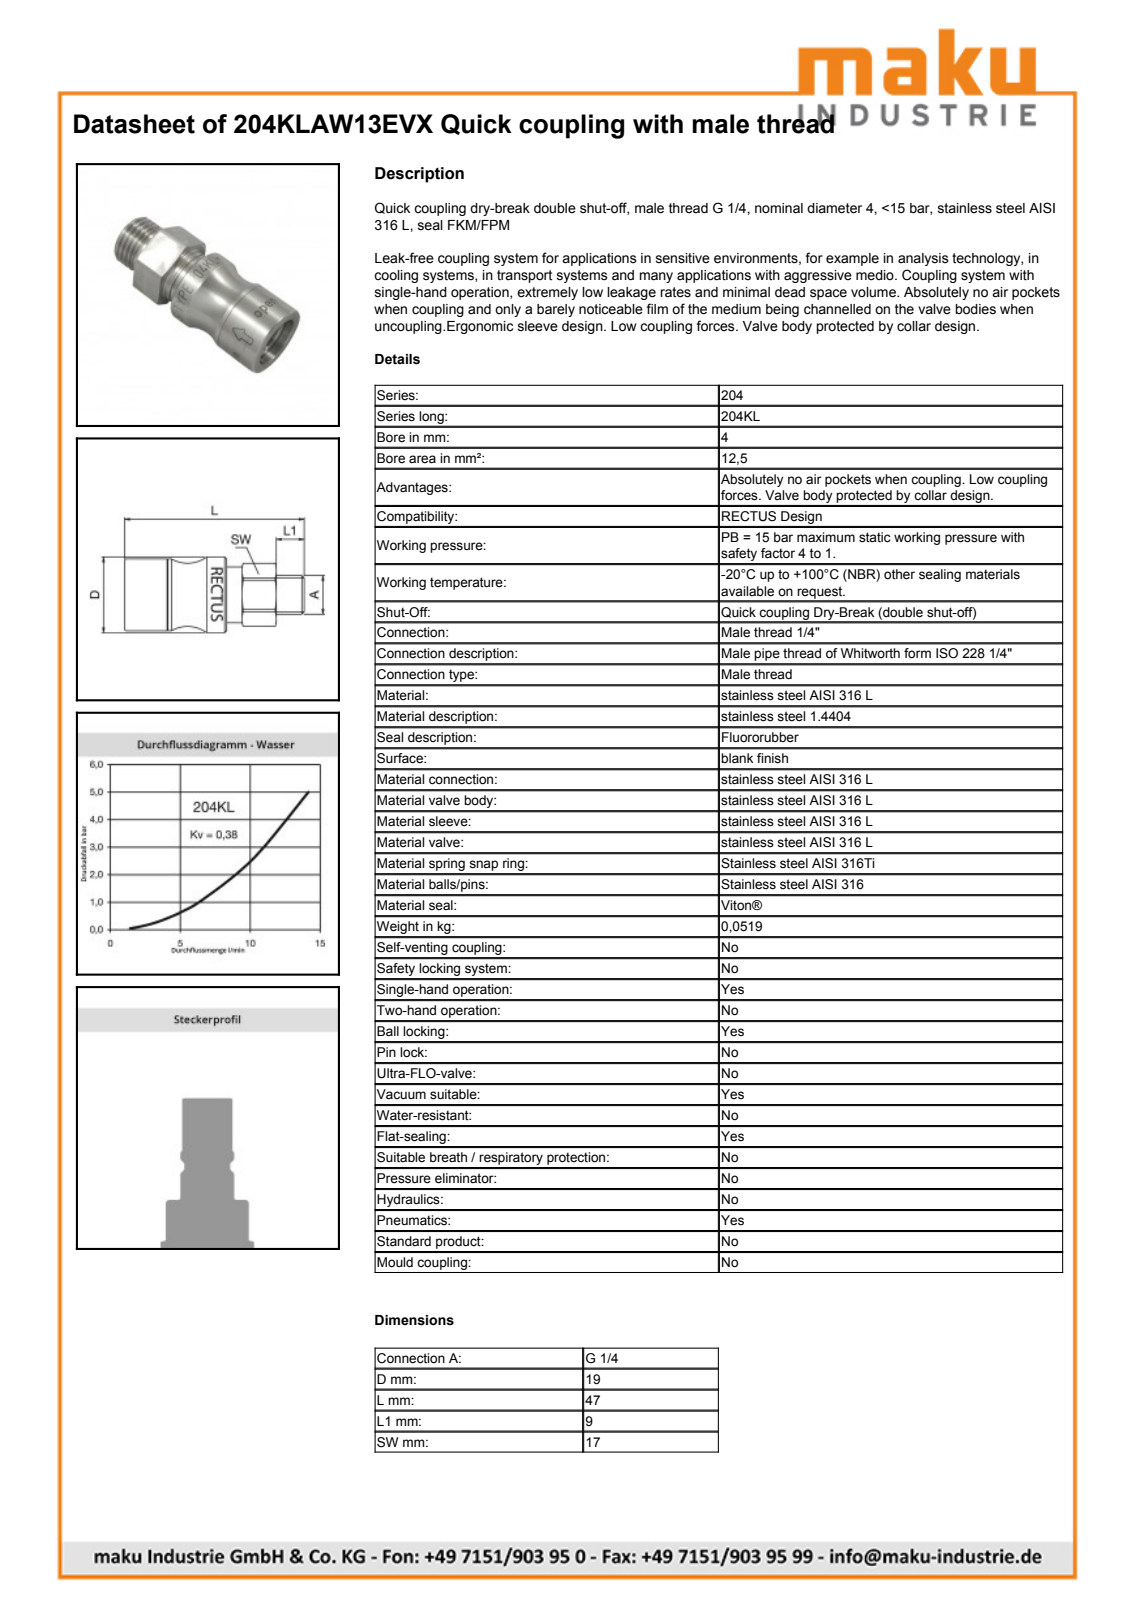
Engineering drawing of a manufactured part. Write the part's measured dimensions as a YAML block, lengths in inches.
part_name: "D110028"
step_written_by: "Autodesk Inventor 2013 (AUTOMOTIVE_DESIGN)"
units: inches
bodies: {solids: 1, faces: 807, planar: 339, cylindrical: 118, other: 350}
overall_size: [1.847, 0.753, 0.748]
volume: 0.539
surface_area: 9.387
round_holes:
  - {diameter: 0.472, count: 1}
  - {diameter: 0.5, count: 1}
  - {diameter: 0.553, count: 1}
  - {diameter: 0.559, count: 1}
  - {diameter: 0.575, count: 1}
  - {diameter: 0.669, count: 1}
  - {diameter: 0.677, count: 1}
round_bosses_or_shafts:
  - {diameter: 0.748, count: 1}
  - {diameter: 0.709, count: 1}
  - {diameter: 0.644, count: 1}
  - {diameter: 0.583, count: 1}
  - {diameter: 0.551, count: 1}
  - {diameter: 0.533, count: 1}
  - {diameter: 0.518, count: 1}
  - {diameter: 0.512, count: 1}
partial_cylinders:
  - {radius: 0.231, count: 1}
  - {radius: 0.35, count: 1}
  - {radius: 0.37, count: 1}
  - {radius: 0.377, count: 1}
face_to_face_distances: [0.669, 1.847, 0.354, 1.007, 0.841, 1.493, 0.486, 1.006, 1.492, 1.846]
